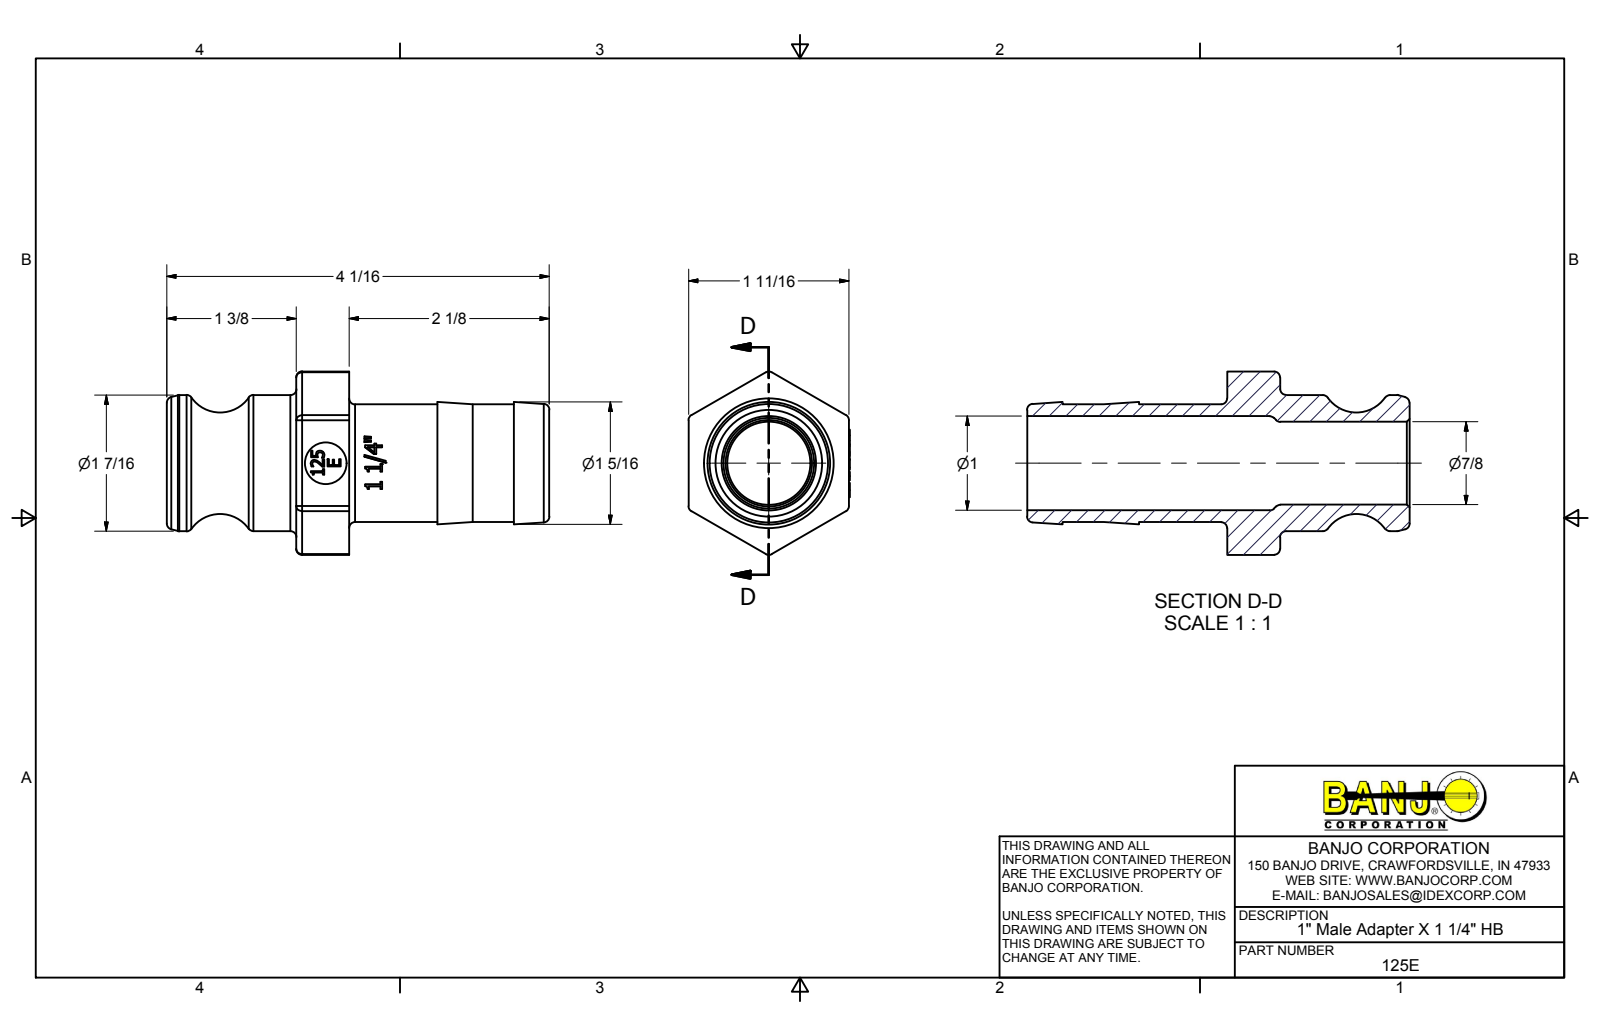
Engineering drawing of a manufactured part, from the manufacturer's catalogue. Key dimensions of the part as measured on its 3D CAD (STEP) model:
Part name (STEP PRODUCT): 125E
STEP written by: Autodesk Inventor 2014 (AUTOMOTIVE_DESIGN)
Units: millimetres
Bodies: 1 solid, 239 faces (135 planar, 26 cylindrical, 78 other)
Overall size (bounding box): 103.19 × 49.46 × 43.51
Volume: 49 488 mm³ · Surface area: 21 550 mm²
Round holes (diameter × count): ⌀11.18 ×1, ⌀22.35 ×1, ⌀25.4 ×1
Round bosses / shafts (diameter × count): ⌀36.73 ×1, ⌀31.75 ×1
Partial cylindrical surfaces — rounded edges, fillets, slot ends (radius × count): R1.59 ×12, R16.13 ×1
Main face-to-face distances: 43.26, 49.21, 103.19, 53.98, 34.92, 14.29, 68.27, 43, 9.53, 73.02
